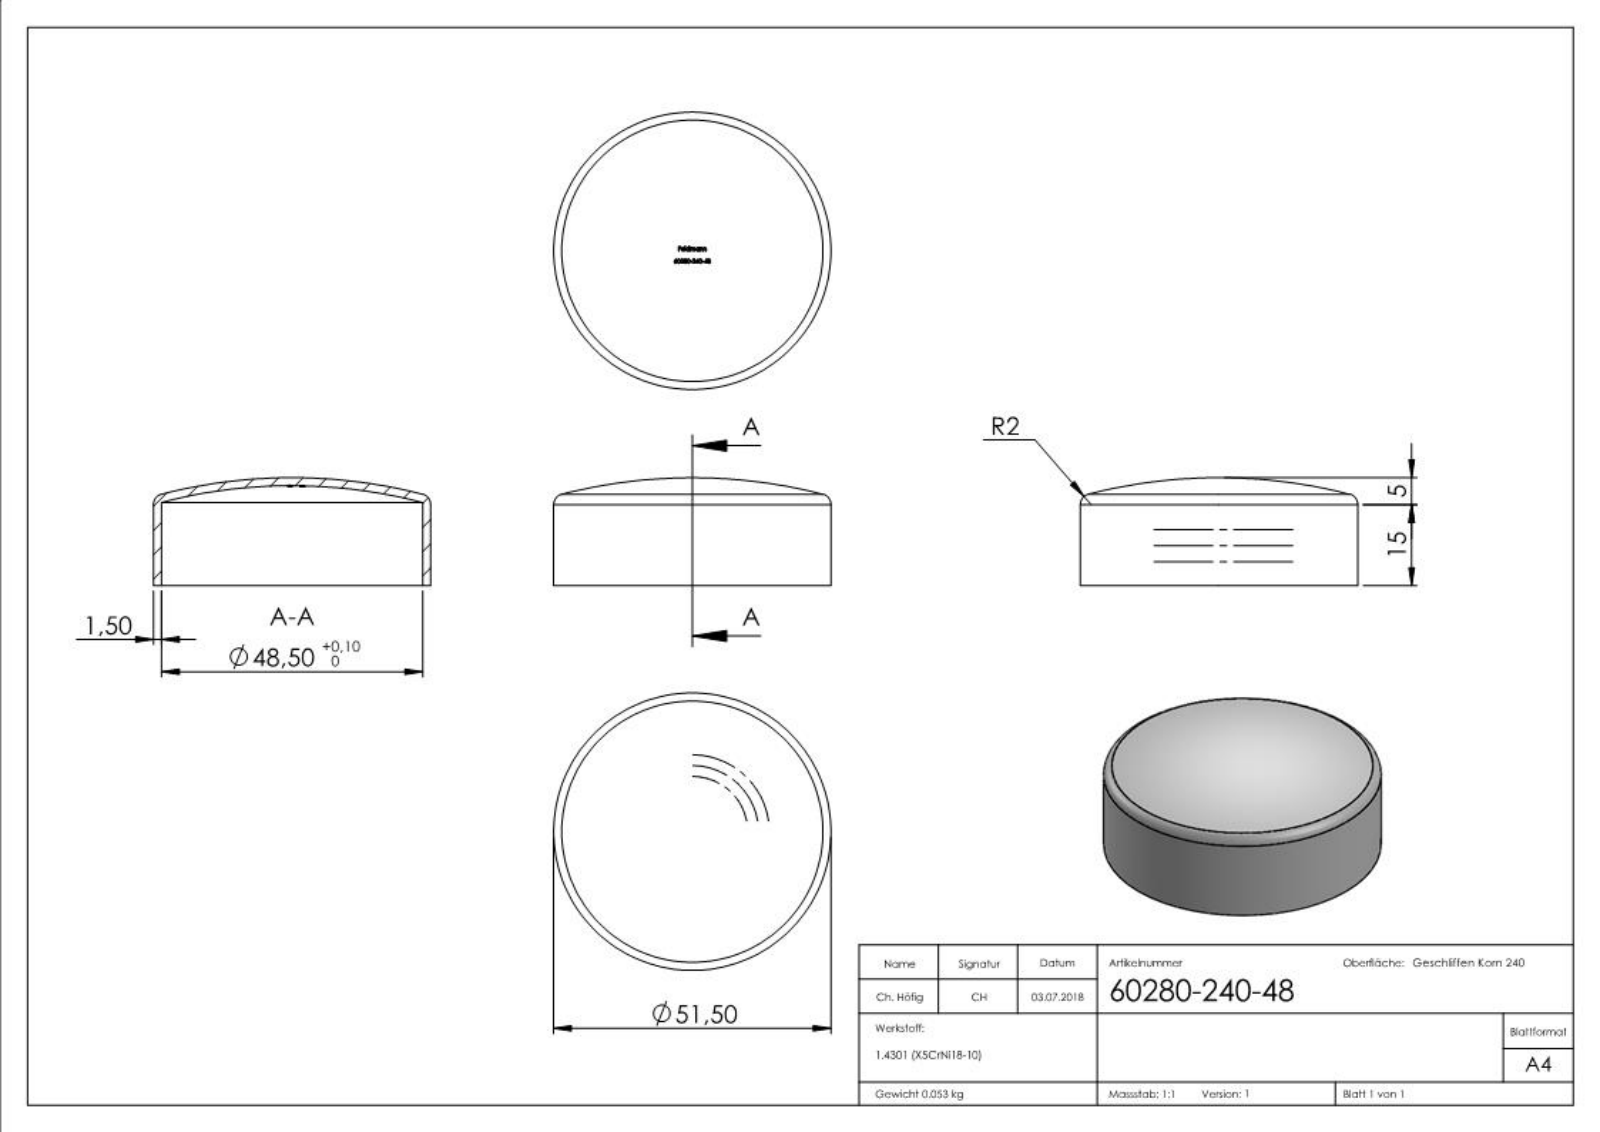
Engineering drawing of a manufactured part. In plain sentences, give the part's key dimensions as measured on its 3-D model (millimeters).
The part is named "60280-240-48". Its 3-D file was written by "SolidWorks 2015 (CONFIG_CONTROL_DESIGN)". It is 1 solid with 286 faces: 104 planar, 4 cylindrical and 178 other. Overall it measures 51.5 by 51.5 by 20 millimeters. Its volume is 6 687 cubic millimeters and its surface area 9 186 square millimeters. Round holes: 1 of diameter 48.5. Round bosses or shafts: 1 of diameter 51.5. The main face-to-face distances are 0.99, 1.78, 0.83, 2.45, 2.38, 1.59, 0.6, 1.06, 1.21, 2.13.
